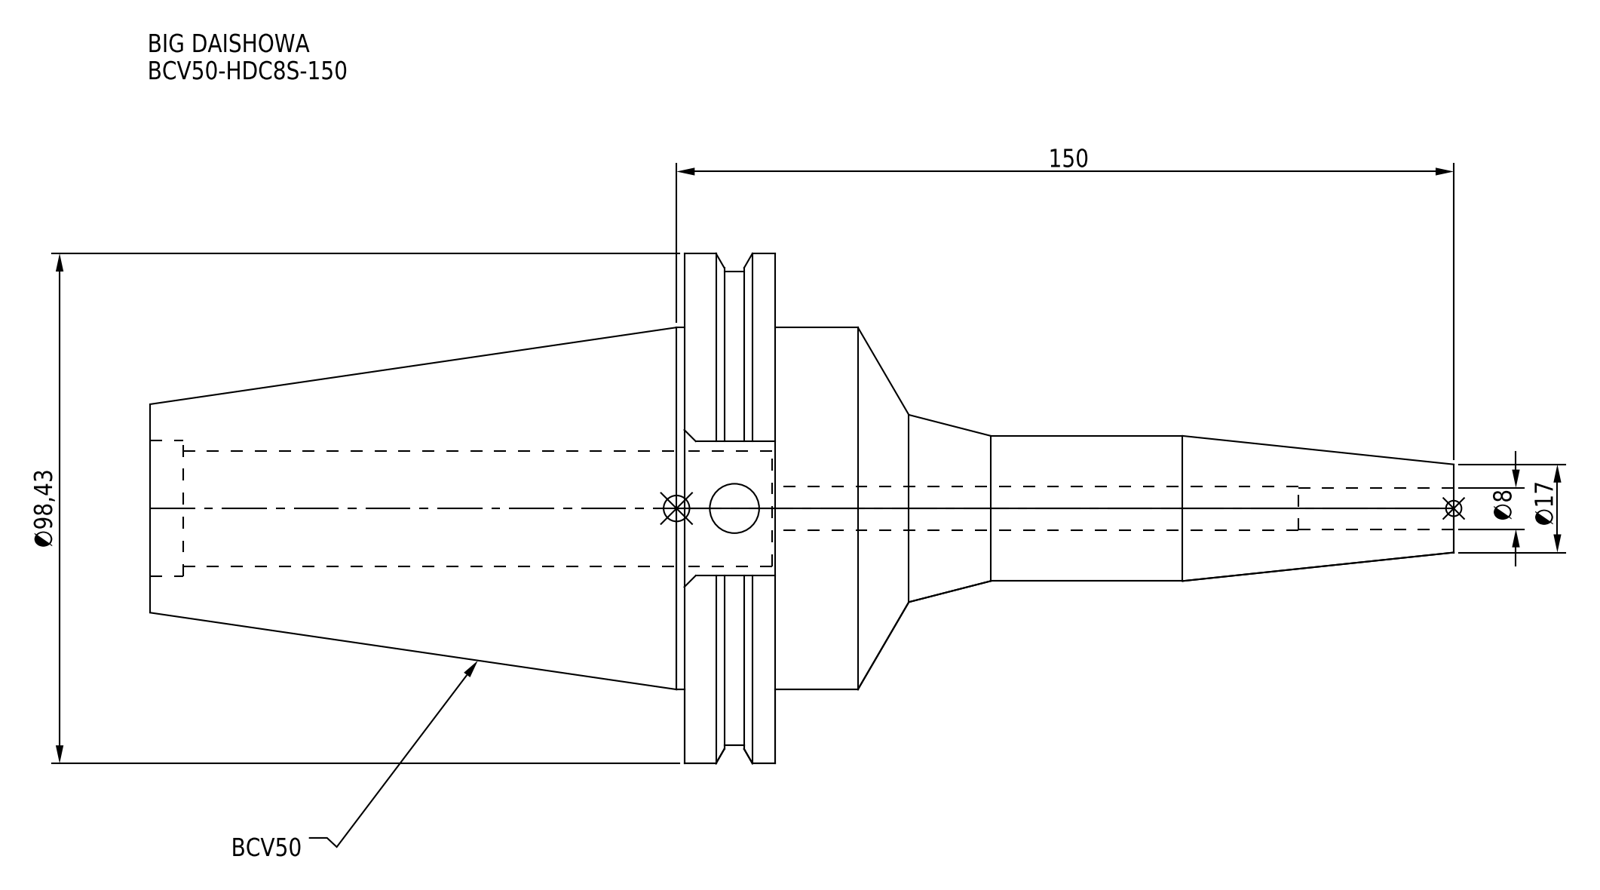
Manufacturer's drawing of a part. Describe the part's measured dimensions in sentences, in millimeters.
The part is named "BCV50-HDC8S-150". Its 3-D file was written by "CREO PARAMETRIC BY PTC INC, 2016380 (AUTOMOTIVE_DESIGN)". It is 1 solid with 58 faces: 22 planar, 24 cylindrical and 12 other. Overall it measures 251.6 by 98.42 by 94.95 millimeters. Its volume is 456 416 cubic millimeters and its surface area 60 212 square millimeters. Round holes: 1 of diameter 8, 1 of diameter 8.5, 1 of diameter 9.53, 1 of diameter 22.3, 1 of diameter 26.23. Round bosses or shafts: 1 of diameter 98.42, 1 of diameter 91.29, 1 of diameter 69.85, 1 of diameter 28. The main face-to-face distances are 17.55, 120.65, 103.1, 72.95, 0.65, 16.9, 120, 25.92, 6, 5.35.
